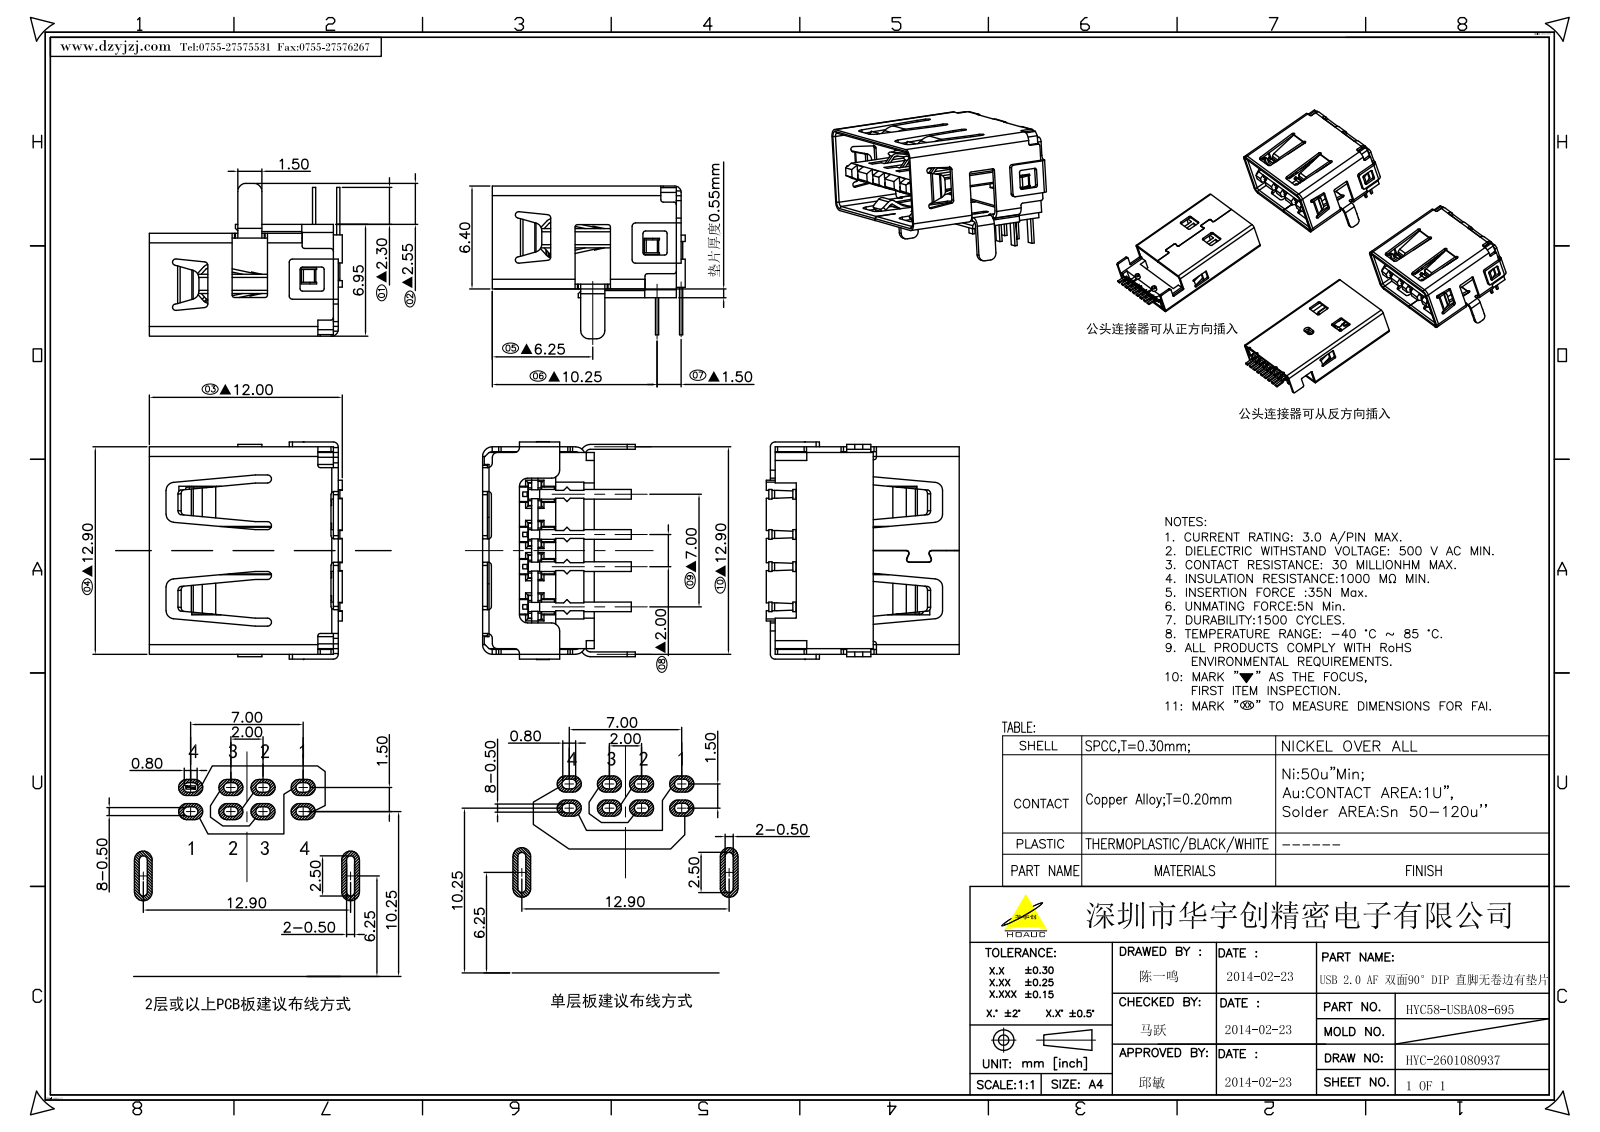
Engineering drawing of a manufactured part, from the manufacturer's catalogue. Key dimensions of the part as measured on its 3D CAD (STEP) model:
Part name (STEP PRODUCT): HOUSING_1
STEP written by: CREO PARAMETRIC BY PTC INC, 2022073 (AUTOMOTIVE_DESIGN)
Units: millimetres
Bodies: 1 solid, 711 faces (466 planar, 221 cylindrical, 24 other)
Overall size (bounding box): 13.55 × 12 × 9.5
Volume: 469 mm³ · Surface area: 1 393 mm²
Partial cylindrical surfaces — rounded edges, fillets, slot ends (radius × count): R0.15 ×32, R0.2 ×24, R0.1 ×21, R0.3 ×20, R0.5 ×17, R0.25 ×12, R0.6 ×10, R0.17 ×8
Main face-to-face distances: 6.1, 3.45, 2.25, 0.55, 2.65, 1.2, 3.55, 2.35, 12.6, 5.8
